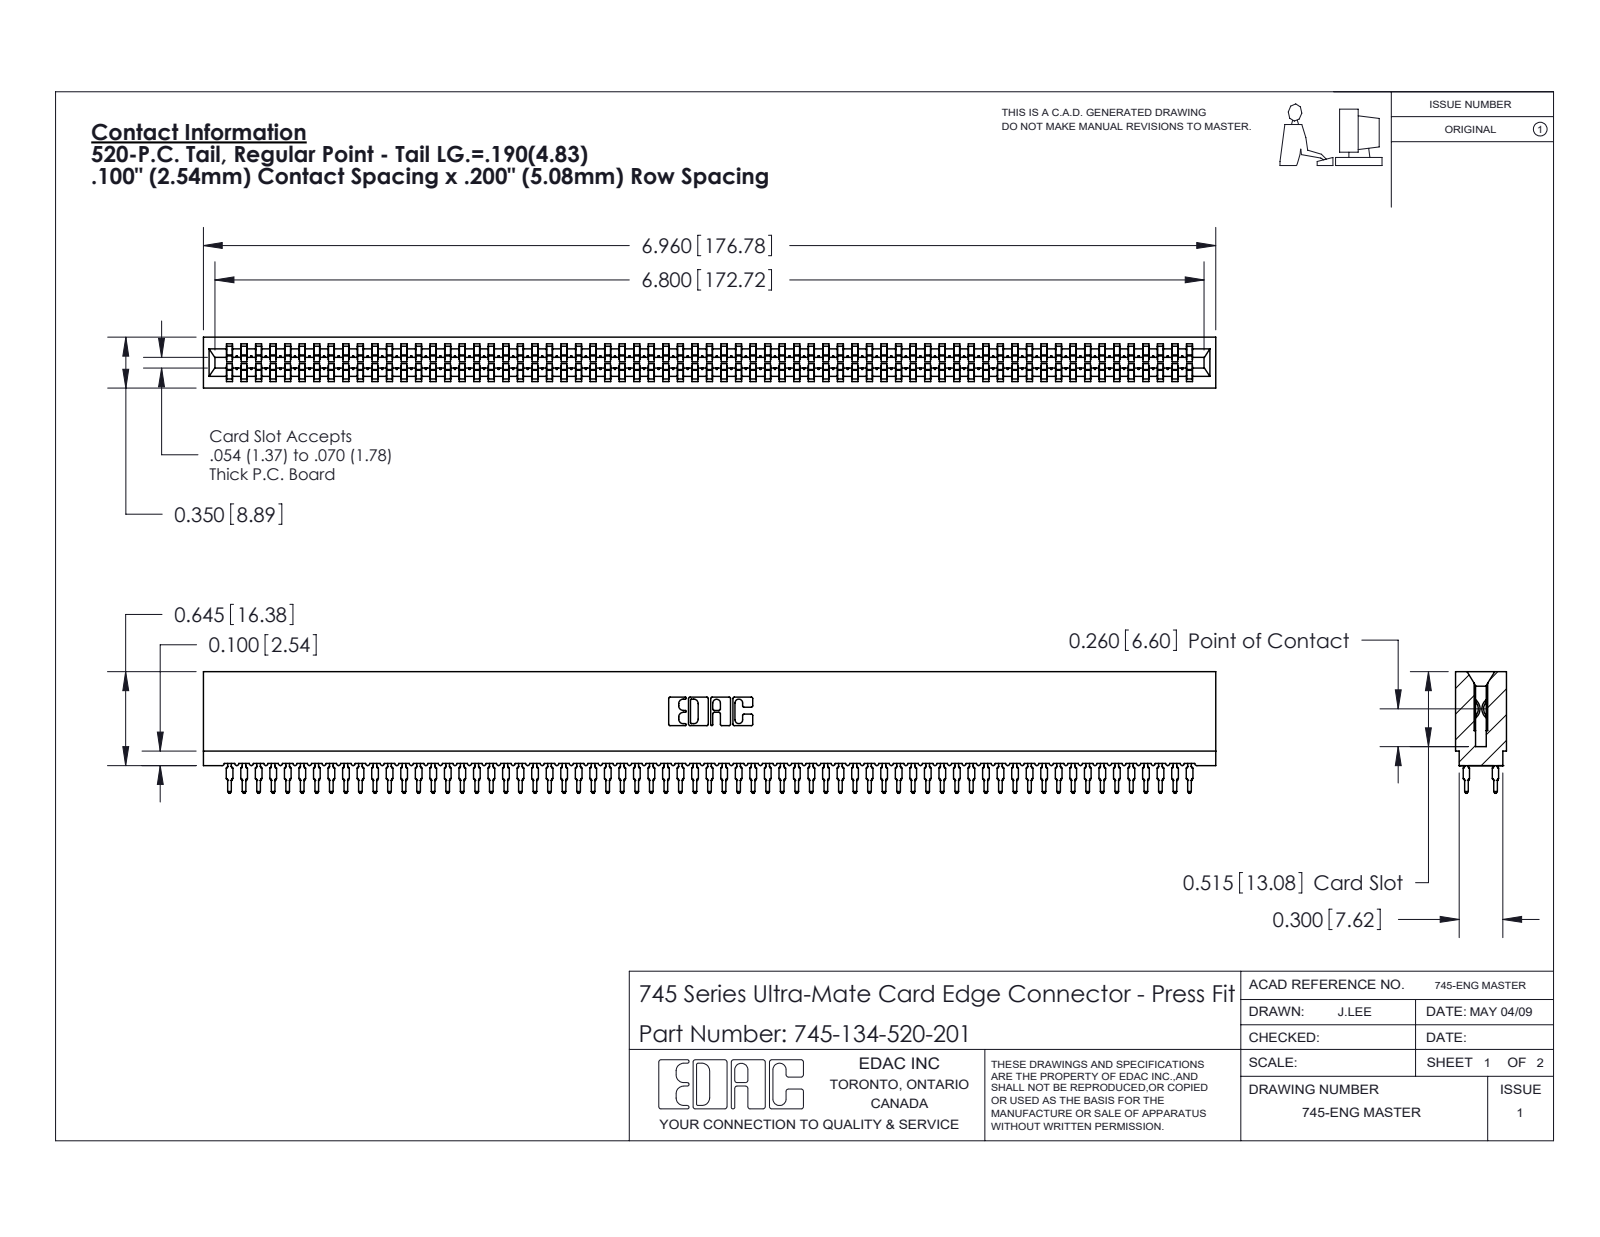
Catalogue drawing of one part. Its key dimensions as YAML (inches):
part_name: "745-292-001_520; 745 Part_Insulator Option - 01; 745-134-520-201"
step_written_by: "SolidWorks 2020 (CONFIG_CONTROL_DESIGN)"
units: inches
bodies: {solids: 135, faces: 12088, planar: 6219, cylindrical: 2385, other: 3484}
overall_size: [6.96, 0.836, 0.35]
volume: 0.956
surface_area: 49.28
partial_cylinders:
  - {radius: 0.021, count: 268}
  - {radius: 0.015, count: 134}
  - {radius: 0.01, count: 22}
  - {radius: 0.005, count: 8}
  - {radius: 0.011, count: 8}
  - {radius: 0.007, count: 6}
  - {radius: 0.031, count: 6}
  - {radius: 0.026, count: 3}
face_to_face_distances: [0.35, 0.063, 0.287, 0.045, 0.305, 0.018, 0.243, 0.138, 0.212, 0.093]
